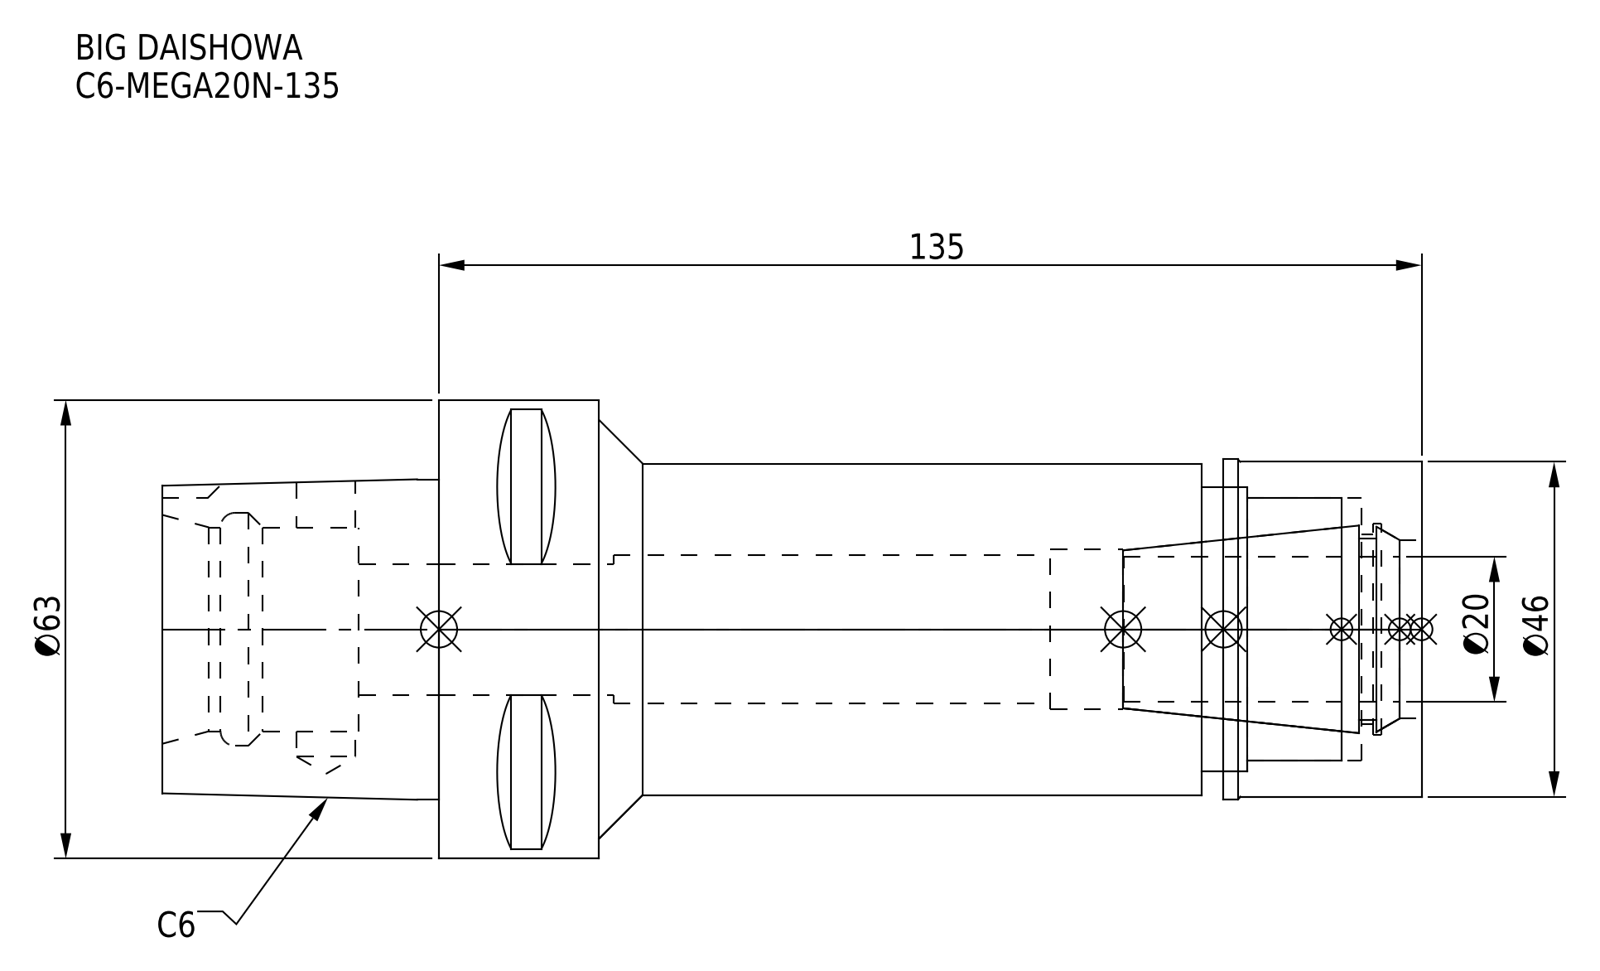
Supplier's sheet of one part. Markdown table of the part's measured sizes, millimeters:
| quantity | value |
| --- | --- |
| part name | MGN20_1.stp; DXF_TEMP_ASSY_ASM_4_ASM.stp; C6-MEGA20N-135-200.stp; C6-MEGA20N-135 (+3 more) |
| STEP written by | SolidWorks 2019 (CONFIG_CONTROL_DESIGN) |
| units | millimeters |
| bodies | 2 solids, 95 faces (38 planar, 39 cylindrical, 18 other) |
| overall size | 173 × 63 × 63 |
| volume | 235 854 mm³ |
| surface area | 49 749 mm² |
| round holes (diameter × count) | 8.1 × 1, 18 × 1, 20.3 × 1, 22 × 1, 24.5 × 1, 26 × 1, 28 × 1, 29 × 1, 32 × 1, 36 × 1, 39 × 1 |
| round bosses / shafts (diameter × count) | 63 × 1, 46.7 × 1, 46 × 1, 45.5 × 1 |
| partial cylindrical surfaces (radius × count) | 5 × 1 |
| main face-to-face distances | 135, 22, 104.8, 11, 60, 113, 27.2, 85.8, 107.8, 173 |
